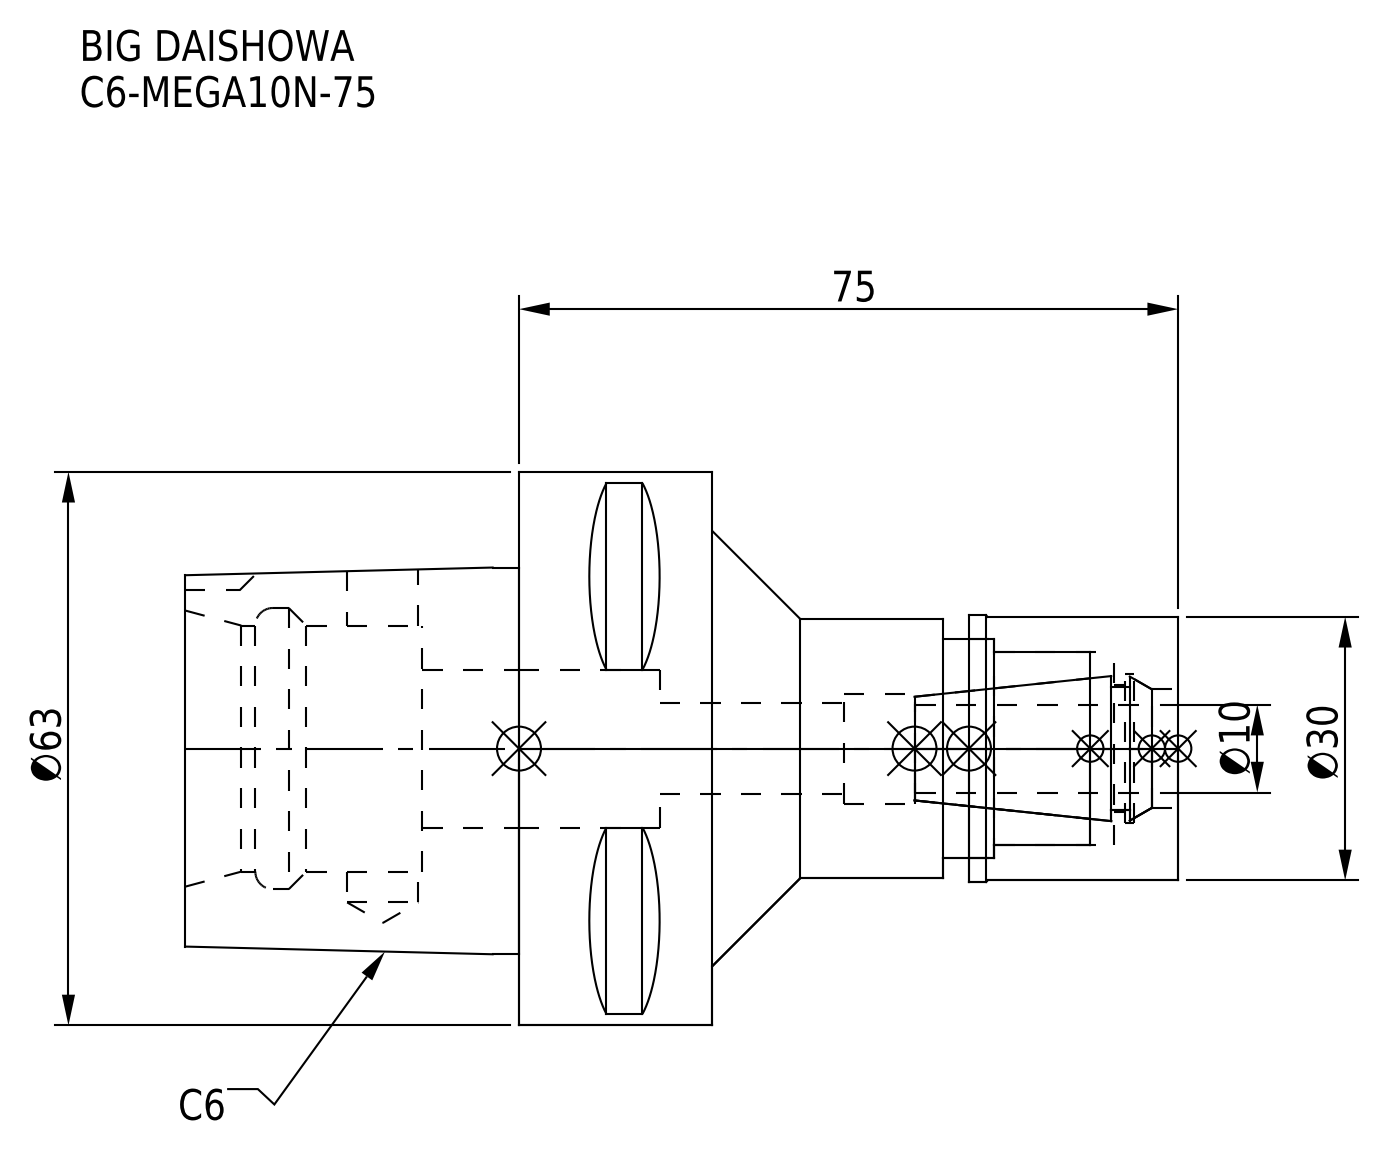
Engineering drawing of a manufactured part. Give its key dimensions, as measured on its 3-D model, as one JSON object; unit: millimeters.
{"part_name": "C6-MEGA10N-75_1.stp; C6-MEGA10N-75-100-FreeParts; MGN10_1.stp; DXF_TEMP_ASSY_ASM_4_ASM.stp (+3 more)", "step_written_by": "SolidWorks 2019 (CONFIG_CONTROL_DESIGN)", "units": "millimeters", "bodies": {"solids": 2, "faces": 95, "planar": 38, "cylindrical": 39, "other": 18}, "overall_size": [113, 63, 63], "volume_mm3": 130414, "surface_area_mm2": 29995, "round_holes": [[8.1, 1], [10.4, 1], [12.5, 1], [13.5, 1], [14.5, 1], [17, 1], [18, 1], [22, 1], [25, 1], [28, 1], [32, 1]], "round_bosses_or_shafts": [[63, 1], [30.3, 1], [30, 1], [29.5, 1]], "partial_cylinders_radius": [[5, 1]], "face_to_face_distances": [22, 53, 75, 38, 27, 113, 60, 33, 86, 11]}
